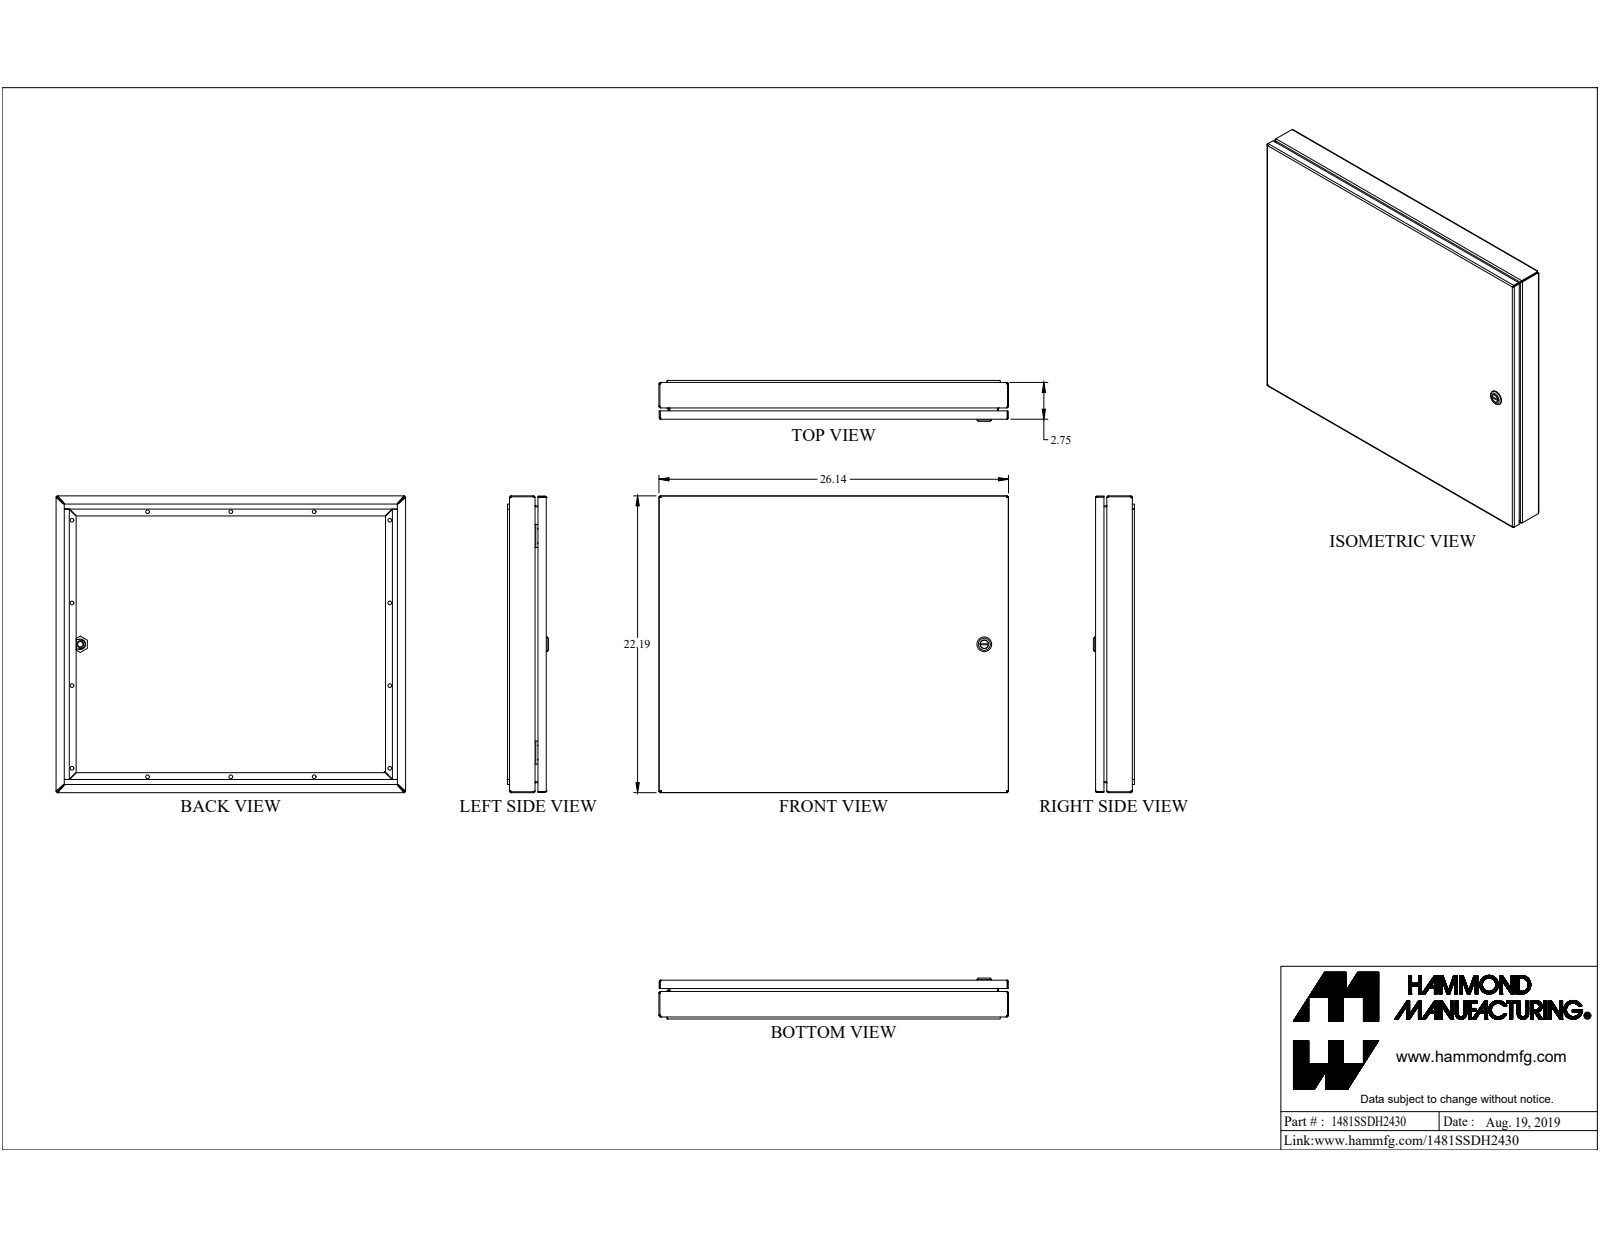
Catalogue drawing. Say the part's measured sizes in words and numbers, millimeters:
The part is named "1481SSDH2430". Its 3-D file was written by "SolidWorks 2019 (CONFIG_CONTROL_DESIGN)". It is 24 solids with 624 faces: 374 planar, 153 cylindrical and 97 other. Overall it measures 664 by 563.6 by 77.7 millimeters. Its volume is 1 561 000 cubic millimeters and its surface area 1 617 000 square millimeters. Round holes: 14 of diameter 7.1, 1 of diameter 4.4, 1 of diameter 5, 1 of diameter 6.1, 1 of diameter 6.1, 1 of diameter 9.8, 1 of diameter 12.7, 1 of diameter 16, 1 of diameter 19.5. Round bosses or shafts: 1 of diameter 27.9, 1 of diameter 19.9, 1 of diameter 15.9, 1 of diameter 13.3, 1 of diameter 12.1, 1 of diameter 10.1, 1 of diameter 9, 1 of diameter 8. Partial cylindrical surfaces (rounded edges, fillets, slot ends): 28 of radius 0.9, 28 of radius 2.7, 4 of radius 0.2, 4 of radius 1.6, 4 of radius 6.4, 4 of radius 12.7, 2 of radius 3.2, 1 of radius 0.5. The main face-to-face distances are 1.8, 65.5, 21.4, 44.1, 67.3, 561.8, 63.7, 662.1, 68, 46.6. The hole center spacings are 623.7, 144.4, 157, 158.2, 302.2, 347.9, 460.3, 491.5.
